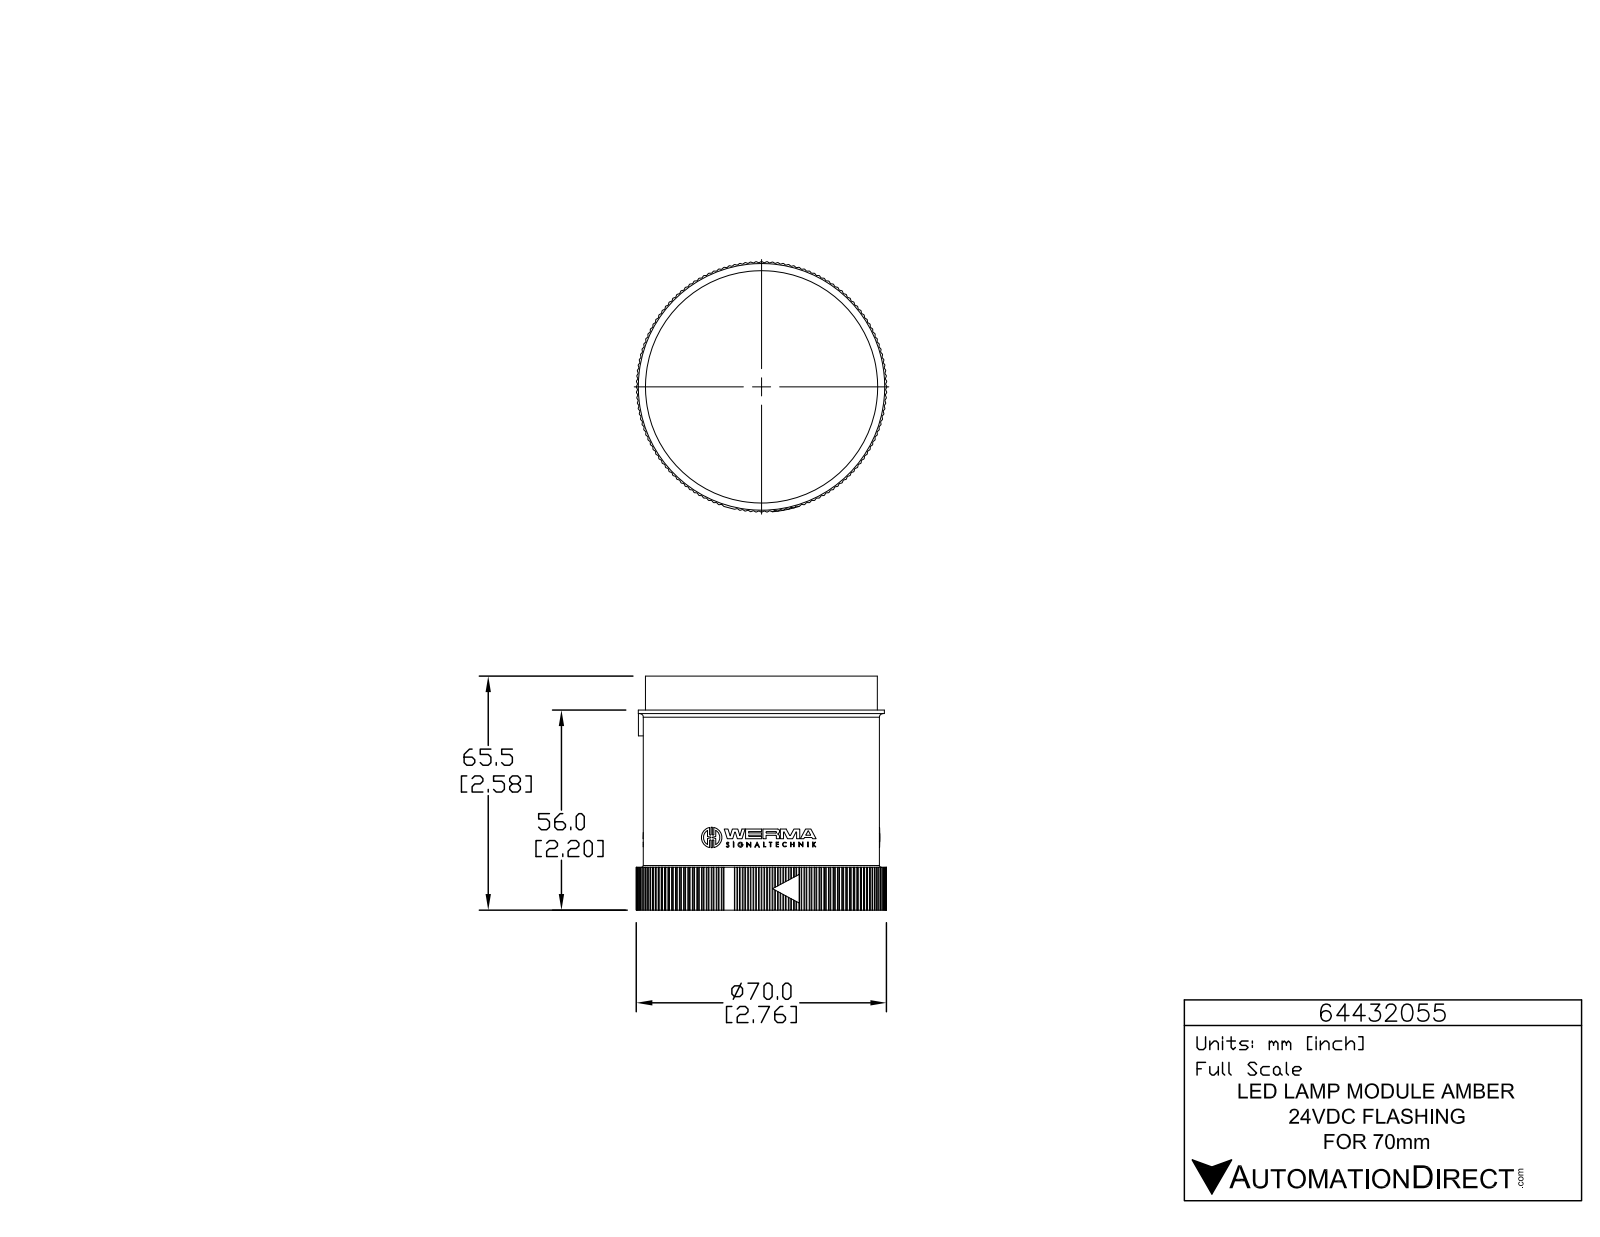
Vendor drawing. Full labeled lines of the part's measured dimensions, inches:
Part name (STEP PRODUCT): 64432055
STEP written by: SolidWorks 2015 (AUTOMOTIVE_DESIGN)
Units: inches
Bodies: 1 solid, 1400 faces (832 planar, 563 cylindrical, 5 other)
Overall size (bounding box): 2.762 × 2.762 × 2.579
Volume: 12.02 in³ · Surface area: 37.48 in²
Round holes (diameter × count): ⌀0.039 ×3, ⌀2.575 ×1
Round bosses / shafts (diameter × count): ⌀0.226 ×3, ⌀0.056 ×3, ⌀2.717 ×1, ⌀2.606 ×1, ⌀2.559 ×1
Partial cylindrical surfaces — rounded edges, fillets, slot ends (radius × count): R0.008 ×285, R0.008 ×6, R0.008 ×6, R0.008 ×6, R0.131 ×6, R0.004 ×3, R0.005 ×3, R0.008 ×3
Main face-to-face distances: 2.201, 2.451, 0.378, 2.579, 2.205, 1.827, 0.374, 2.452, 0.472, 0.094
